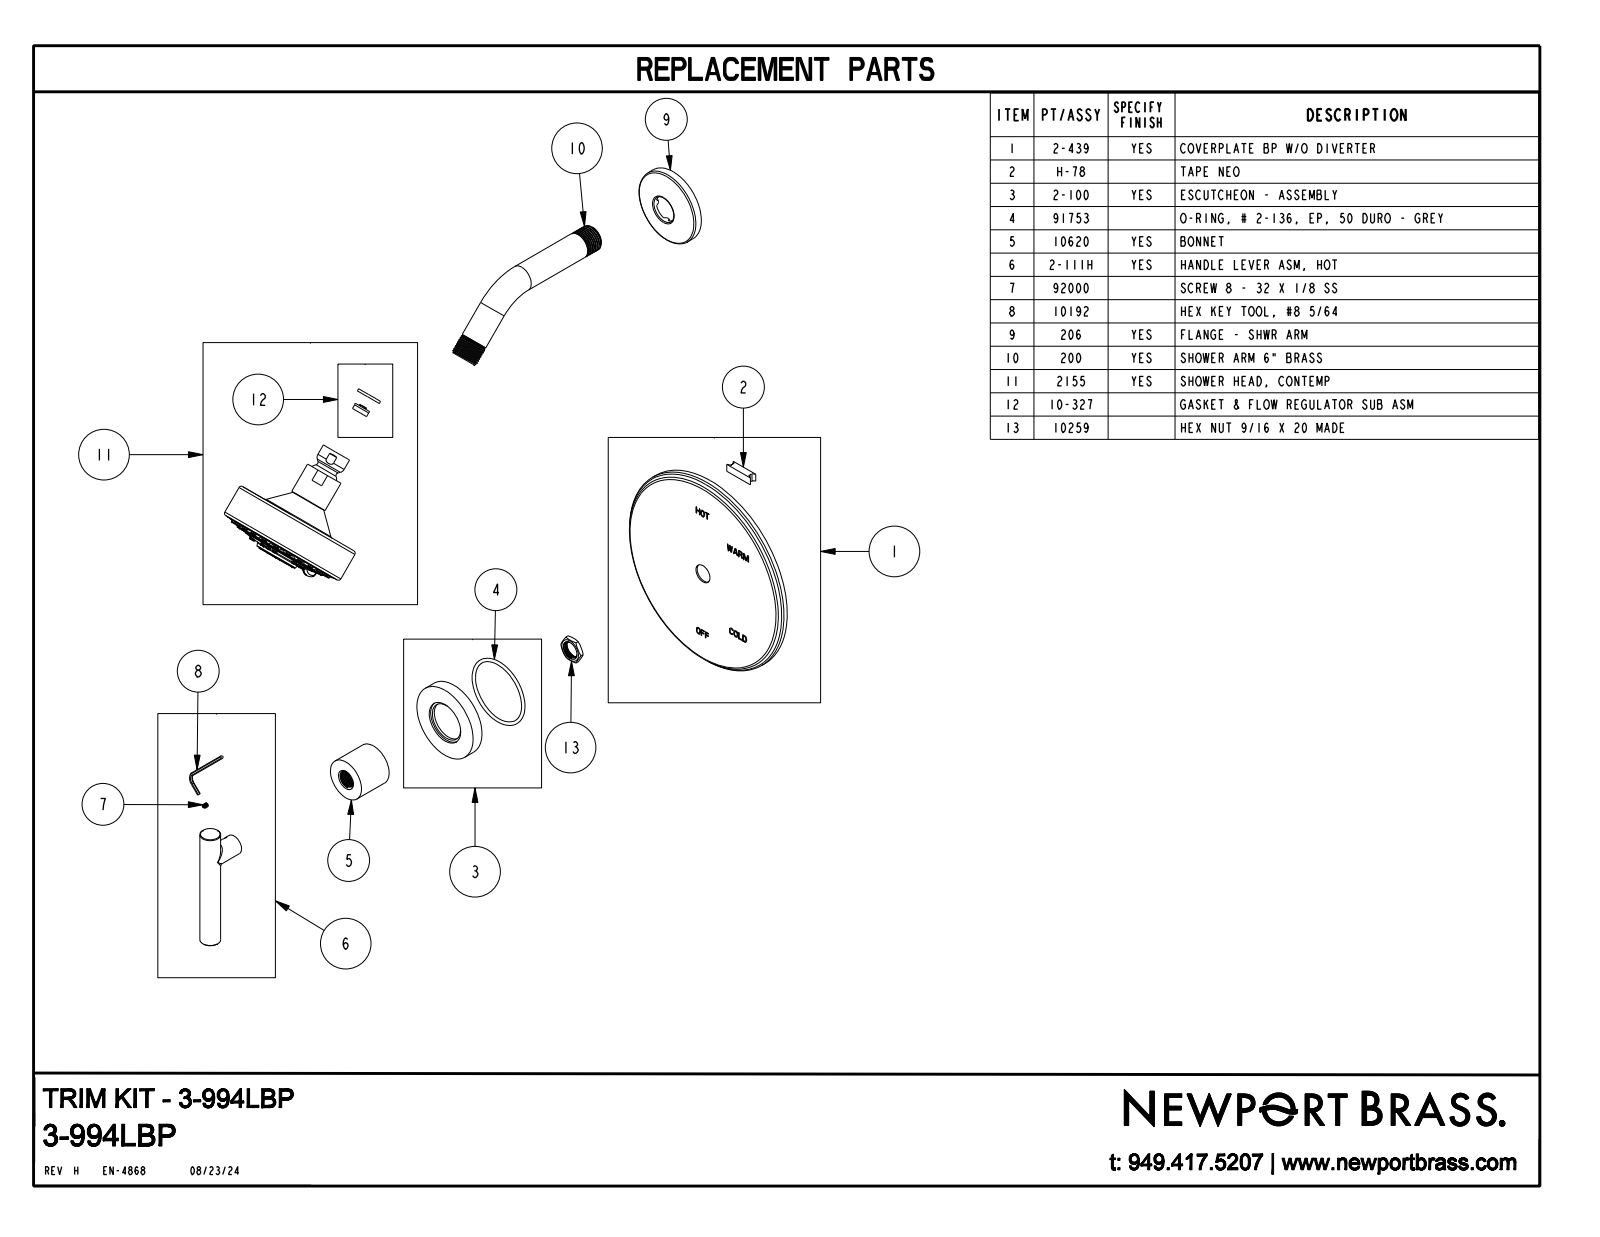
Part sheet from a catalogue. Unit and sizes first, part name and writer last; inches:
Units: inches
Overall size (bounding box): 16.44 × 8.175 × 6.5
Round holes (diameter × count): ⌀0.059 ×8, ⌀0.925 ×1
Round bosses / shafts (diameter × count): ⌀0.142 ×39, ⌀0.165 ×23, ⌀0.813 ×2, ⌀0.625 ×2, ⌀6.5 ×1, ⌀4 ×1, ⌀3.724 ×1, ⌀2.38 ×1
Partial cylindrical surfaces — rounded edges, fillets, slot ends (radius × count): R0.079 ×8, R0.02 ×2, R0.138 ×1, R0.472 ×1, R0.512 ×1, R0.63 ×1
Main face-to-face distances: 0.313, 0.688, 0.375, 1.796, 1.483, 1.108, 1.147, 0.063, 1.211, 0.118
Hole centre spacings: 0.443, 0.579, 0.818, 0.819, 1.069, 0.443, 0.578, 1.069
Volume: 35.26 in³ · Surface area: 161.5 in²
Bodies: 2 solids, 1403 faces (465 planar, 203 cylindrical, 735 other)
Part name (STEP PRODUCT): 3-994LBP
STEP written by: CREO PARAMETRIC BY PTC INC, 2018400 (CONFIG_CONTROL_DESIGN)
